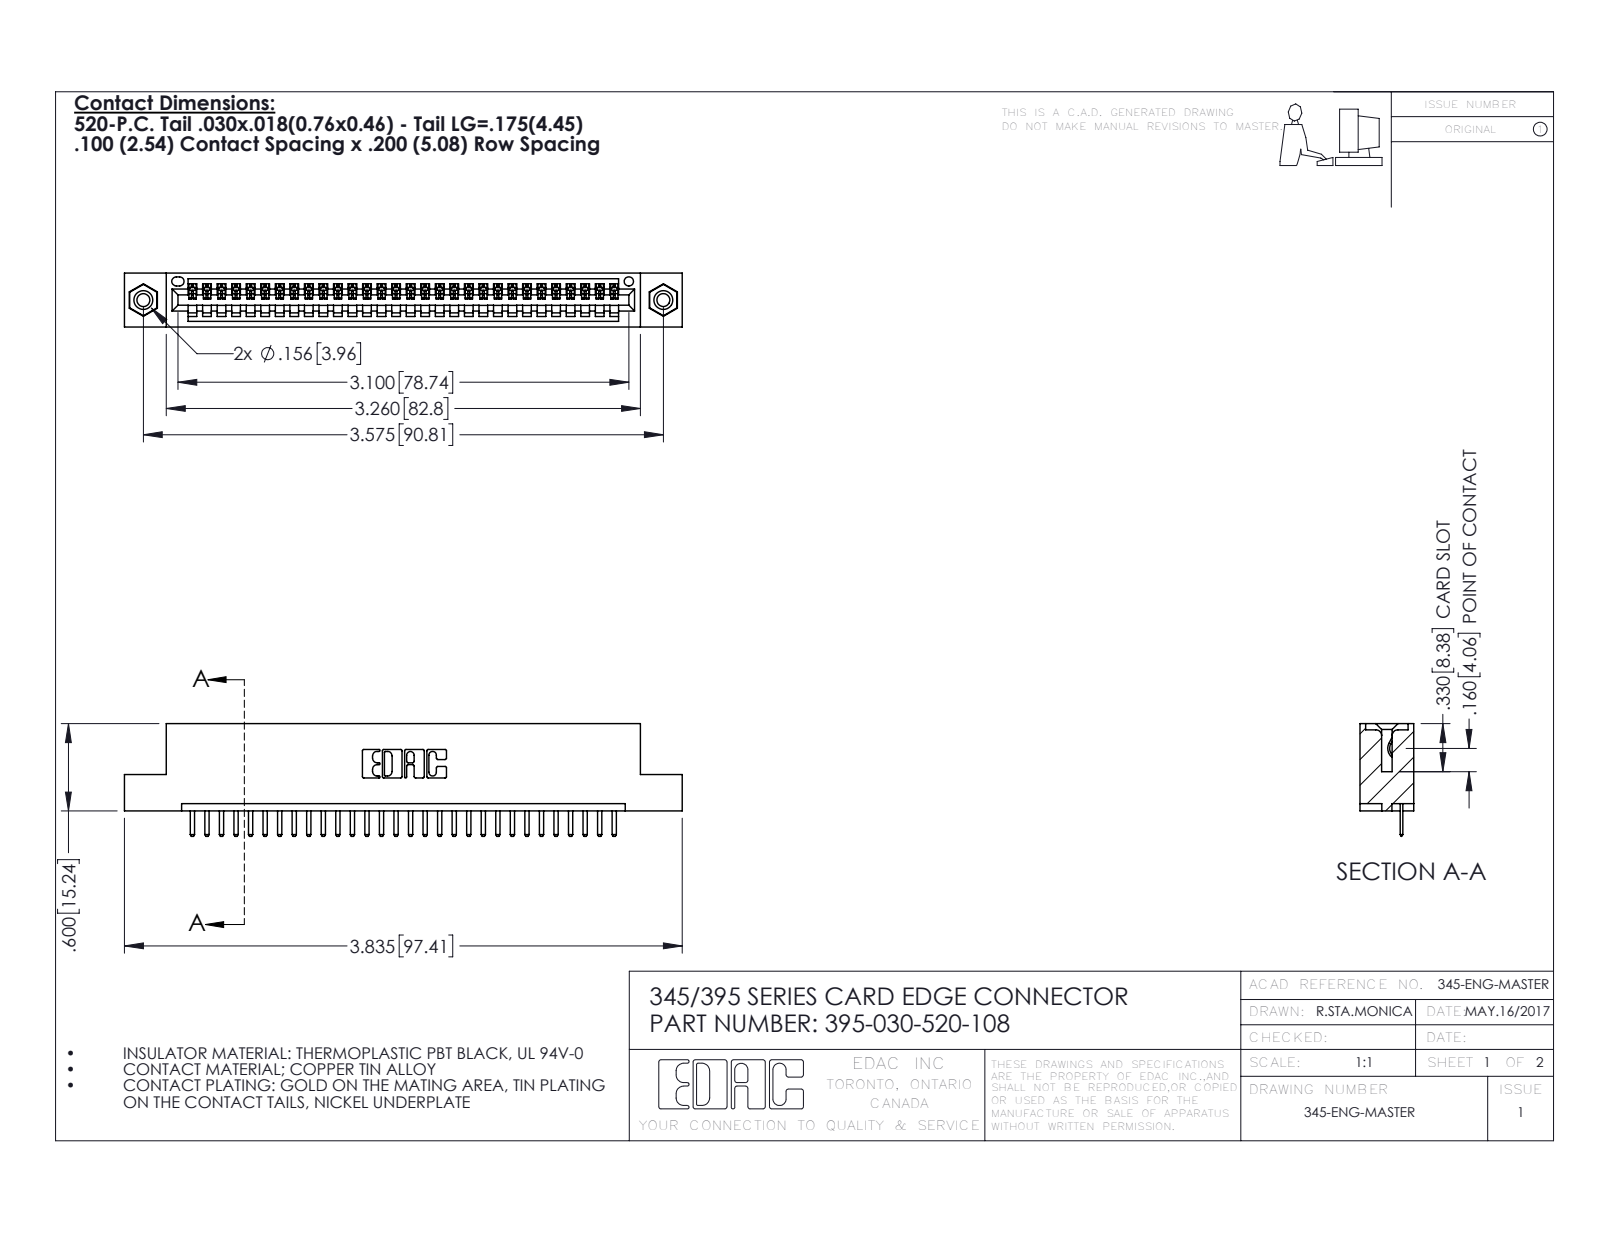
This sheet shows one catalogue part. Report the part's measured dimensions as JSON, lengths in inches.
{"part_name": "345-292-001_345-293-120; 395-030-520-108; 345-250-001_345-250-003-102; 345 Part_Flush Mounting Lugs - 0.156 Dia-TI", "step_written_by": "SolidWorks 2016 (CONFIG_CONTROL_DESIGN)", "units": "inches", "bodies": {"solids": 33, "faces": 2046, "planar": 1372, "cylindrical": 658, "other": 16}, "overall_size": [3.835, 0.775, 0.37], "volume_in3": 0.553, "surface_area_in2": 18, "round_holes": [[0.089, 2], [0.125, 2], [0.156, 2], [0.064, 1]], "round_bosses_or_shafts": [[0.155, 2]], "partial_cylinders_radius": [[0.01, 62], [0.006, 60], [0.01, 22], [0.007, 6], [0.031, 6], [0.026, 3], [0.031, 2], [0.04, 2]], "face_to_face_distances": [0.072, 0.298, 0.37, 0.2, 0.098, 0.272, 0.025, 0.225, 0.072, 0.149], "hole_center_spacings": [0.27, 3.34, 3.575]}
